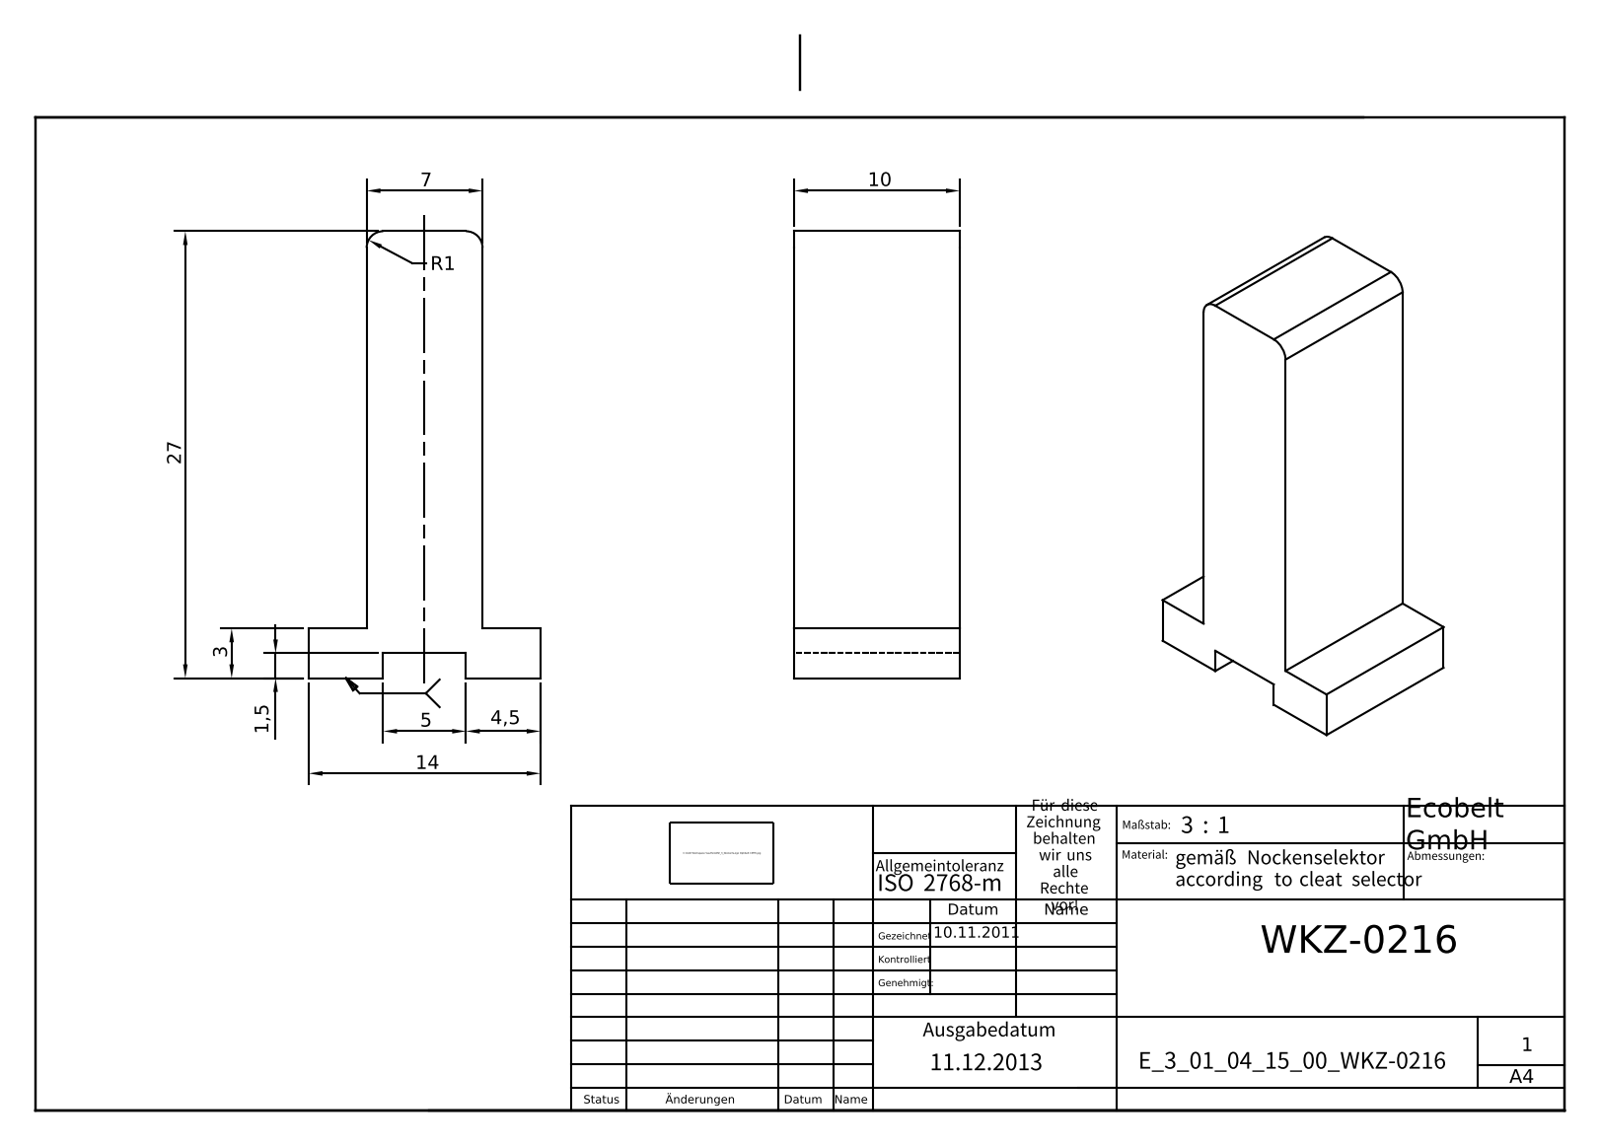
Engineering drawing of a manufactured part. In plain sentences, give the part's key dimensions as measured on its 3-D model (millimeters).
The part is named "E_3_01_04_15_00_WKZ-0216". Its 3-D file was written by "Autodesk Inventor 2025 (AUTOMOTIVE_DESIGN)". It is 1 solid with 16 faces: 14 planar, 2 cylindrical and 0 other. Overall it measures 27 by 14 by 10 millimeters. Its volume is 2 021 cubic millimeters and its surface area 1 246 square millimeters. Partial cylindrical surfaces (rounded edges, fillets, slot ends): 2 of radius 1. The main face-to-face distances are 7, 10, 1.5, 3, 3.5, 10.5, 27, 25.5, 24, 14.
